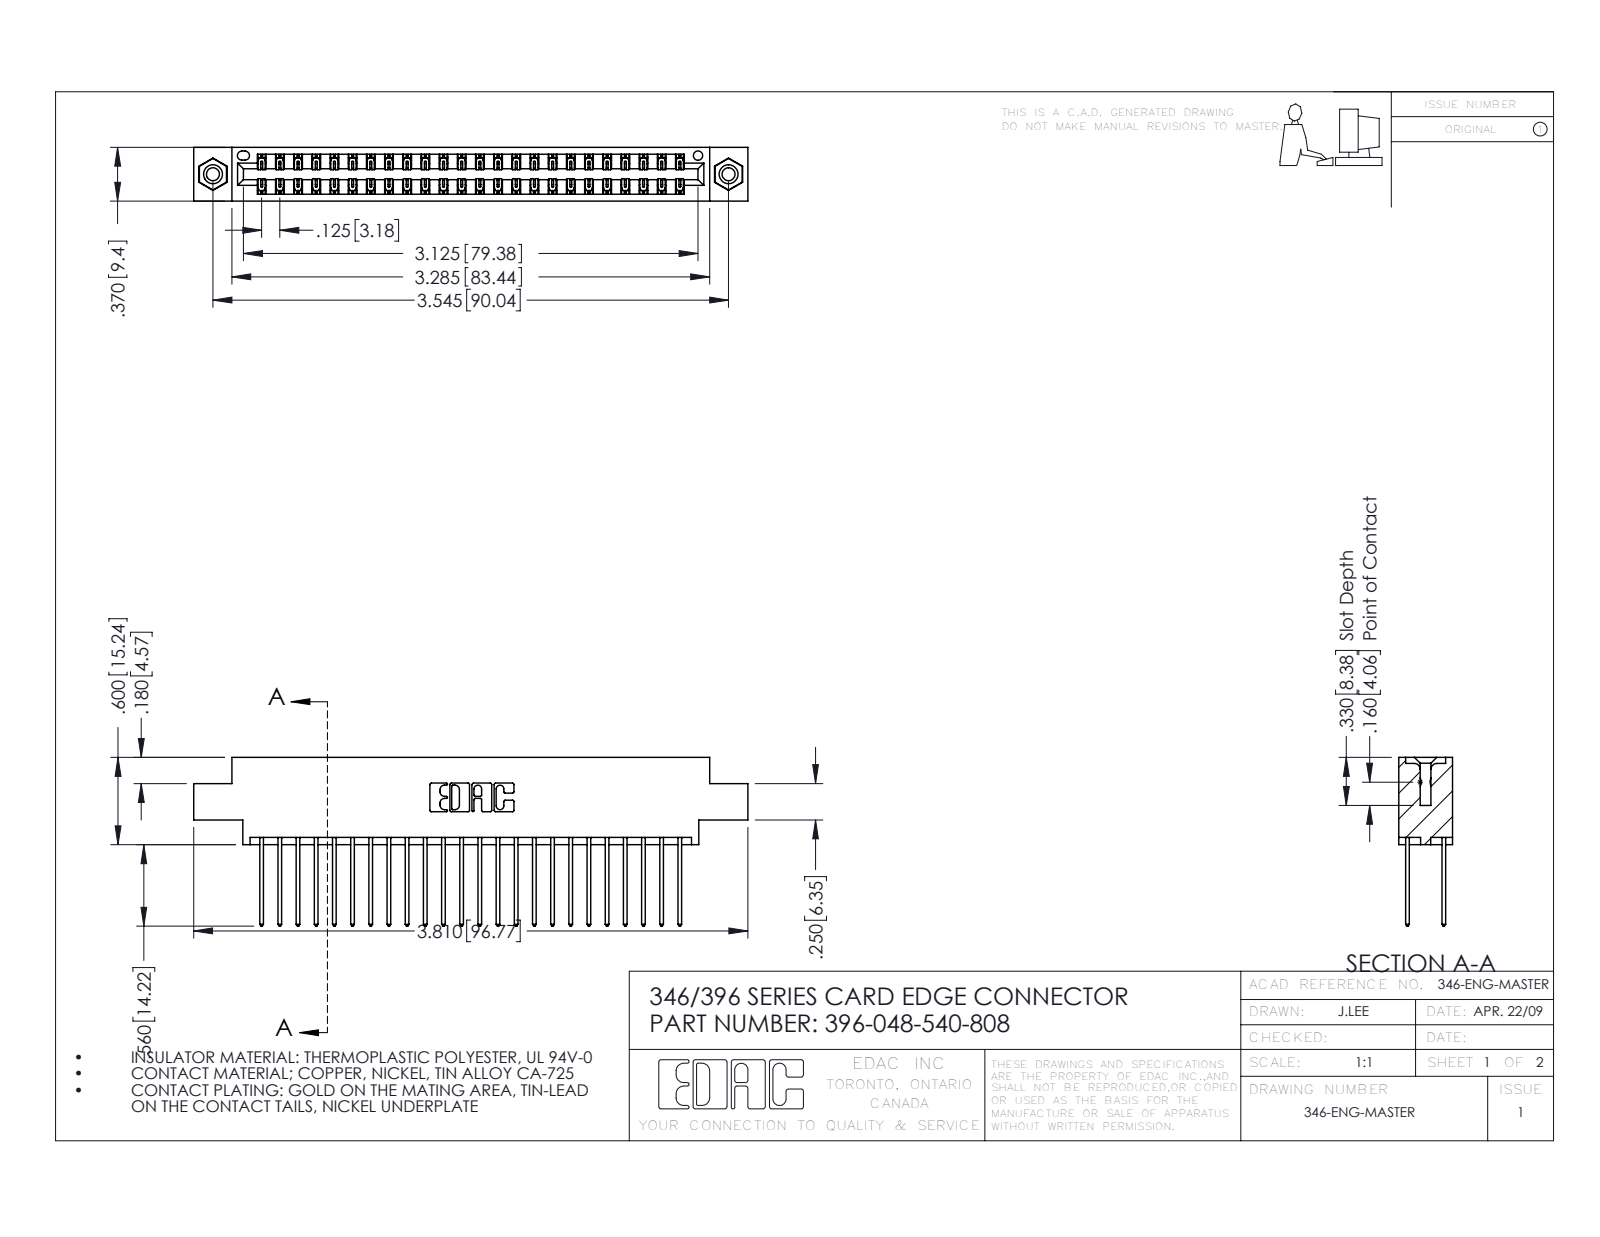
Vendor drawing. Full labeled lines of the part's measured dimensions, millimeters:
Part name (STEP PRODUCT): 346 Part_0.170 Offset - 0.156 Dia-TI; 345-292-001_345-293-140; 396-048-540-808; 345-250-001_345-250-003-102
STEP written by: SolidWorks 2016 (CONFIG_CONTROL_DESIGN)
Units: millimetres
Bodies: 51 solids, 2682 faces (1792 planar, 874 cylindrical, 16 other)
Overall size (bounding box): 96.8 × 29.5 × 9.4
Volume: 9 320 mm³ · Surface area: 13 590 mm²
Round holes (diameter × count): ⌀2.3 ×2, ⌀3.2 ×2, ⌀4 ×2, ⌀1.6 ×1
Round bosses / shafts (diameter × count): ⌀3.9 ×2
Partial cylindrical surfaces — rounded edges, fillets, slot ends (radius × count): R0.2 ×72, R0.3 ×48, R0.3 ×22, R0.2 ×6, R0.8 ×6, R0.7 ×3, R0.4 ×2, R0.6 ×2
Main face-to-face distances: 1.2, 8.2, 6.4, 9.4, 1.8, 7.6, 0.6, 7, 5.6, 3.8
Hole centre spacings: 6.2, 84.8, 90
